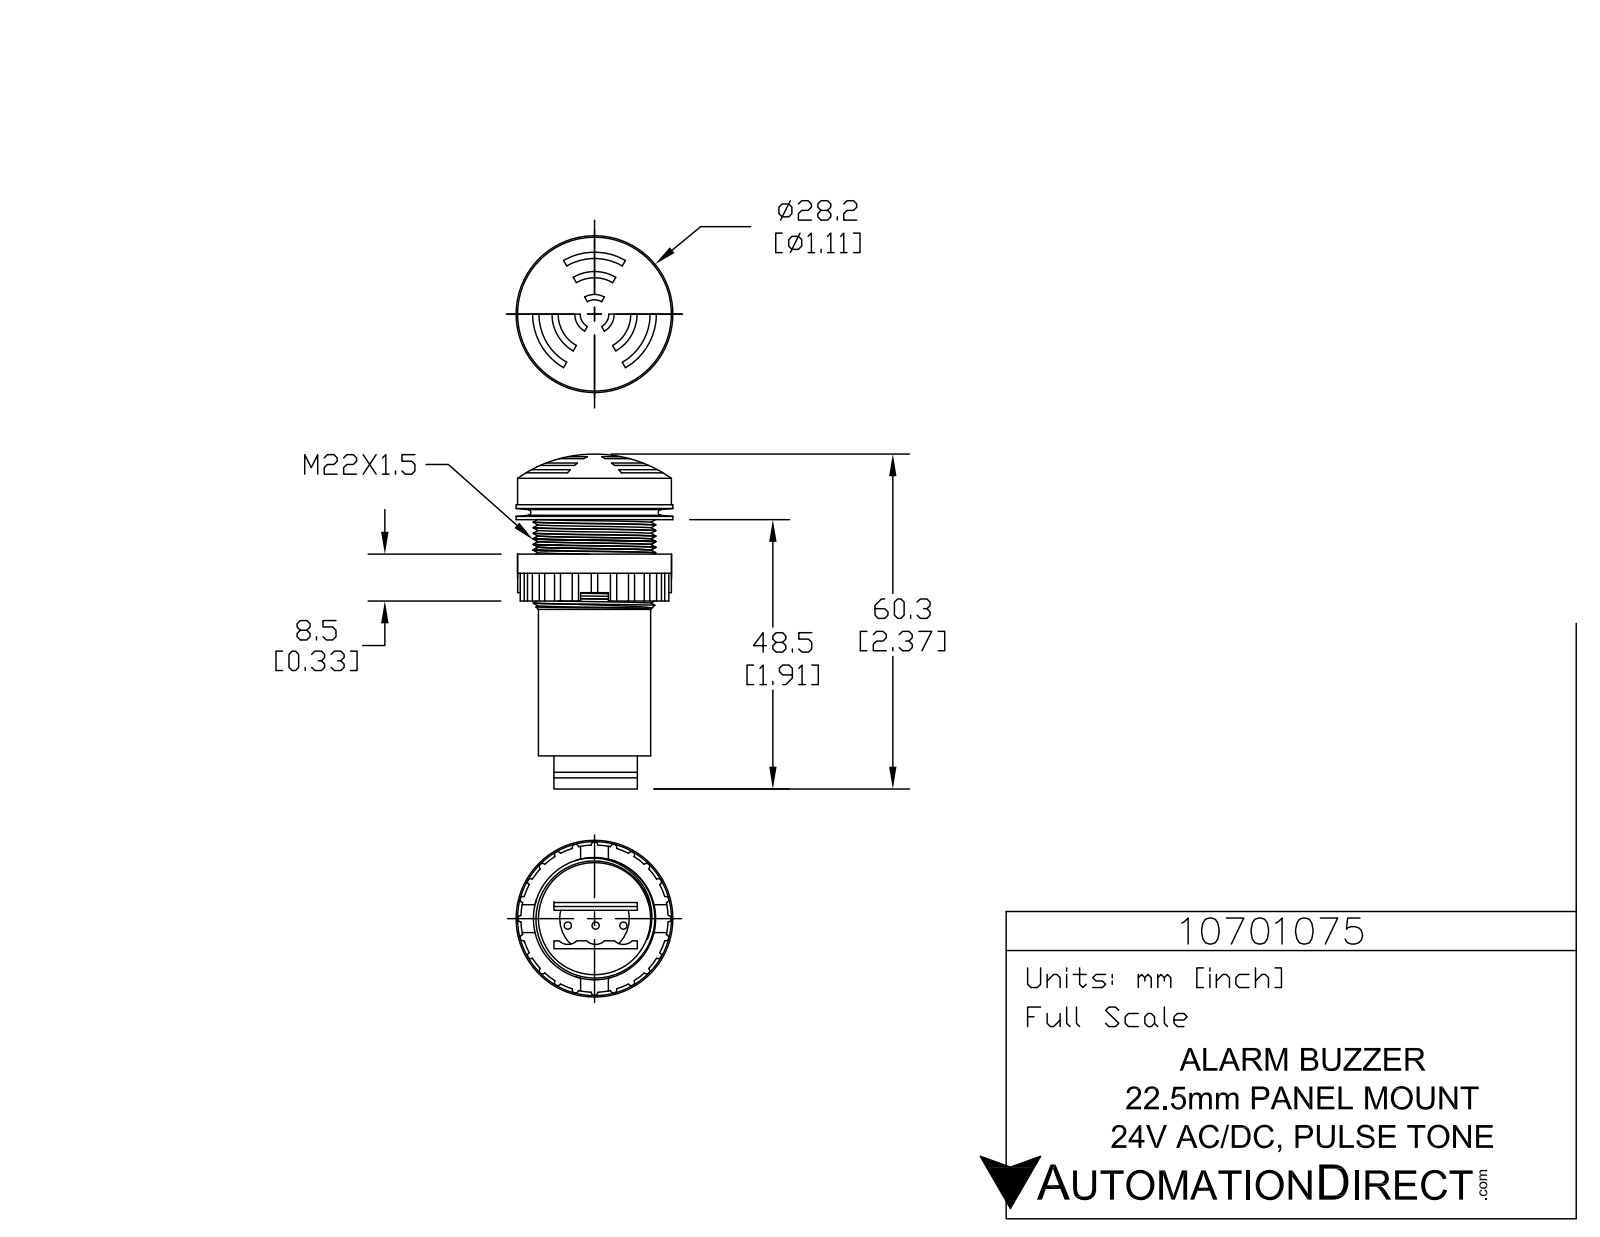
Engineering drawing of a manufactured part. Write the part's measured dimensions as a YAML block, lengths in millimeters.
part_name: "10701075"
step_written_by: "SolidWorks 2017 (AUTOMOTIVE_DESIGN)"
units: millimeters
bodies: {solids: 1, faces: 161, planar: 37, cylindrical: 103, other: 21}
overall_size: [59.4, 28.2, 28.2]
volume: 21583
surface_area: 7928
round_bosses_or_shafts:
  - {diameter: 1.3, count: 3}
  - {diameter: 28.2, count: 1}
  - {diameter: 27.7, count: 1}
  - {diameter: 22, count: 1}
  - {diameter: 20.2, count: 1}
partial_cylinders:
  - {radius: 0.57, count: 24}
  - {radius: 2.25, count: 3}
  - {radius: 6.25, count: 1}
  - {radius: 13.25, count: 1}
face_to_face_distances: [35.5, 8.5, 27, 6.9, 32.95, 3.5, 41.65, 14.65, 6.15, 2.55]
